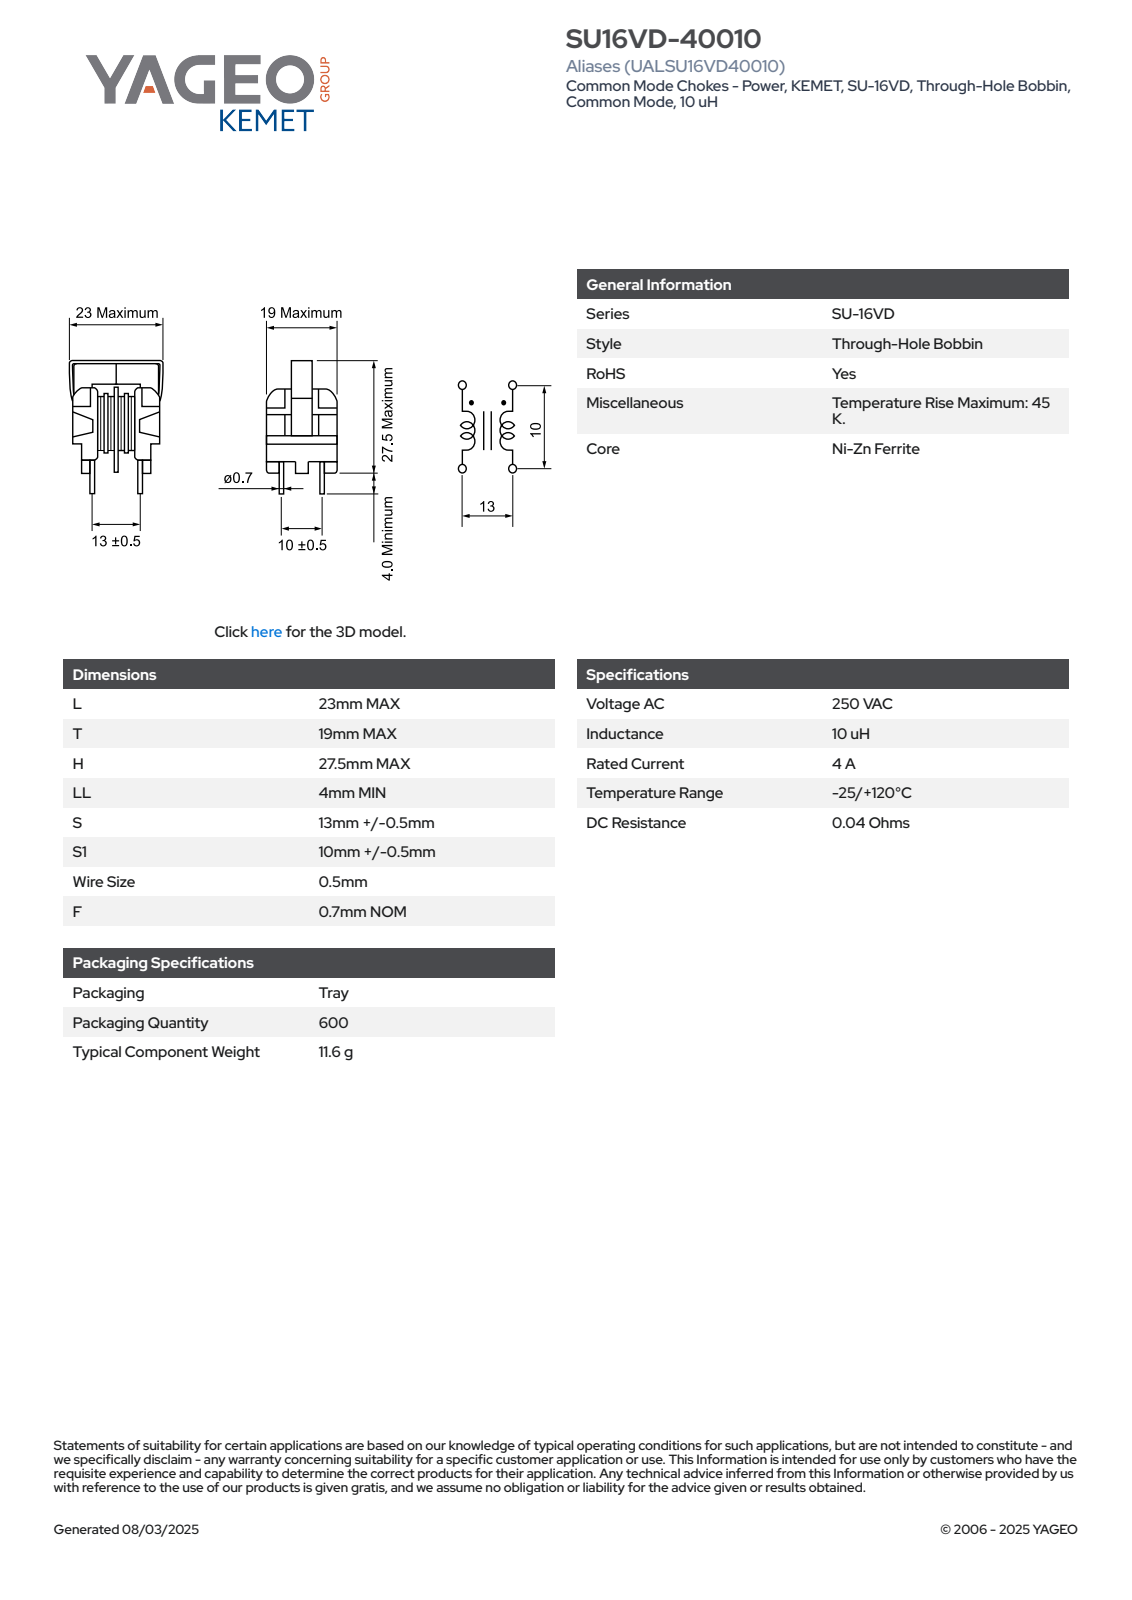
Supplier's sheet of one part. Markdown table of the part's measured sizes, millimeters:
| quantity | value |
| --- | --- |
| part name | SU16VD(MAX-LOGO) |
| STEP written by | SolidWorks 2018 (AUTOMOTIVE_DESIGN) |
| units | millimeters |
| bodies | 4 solids, 521 faces (232 planar, 211 cylindrical, 78 other) |
| overall size | 32 × 23 × 19 |
| volume | 4 325 mm³ |
| surface area | 5 415 mm² |
| round bosses / shafts (diameter × count) | 0.7 × 4 |
| partial cylindrical surfaces (radius × count) | 0.36 × 48, 0.5 × 32, 0.8 × 12, 0.4 × 8, 0.2 × 4, 0.3 × 2, 2.5 × 2, 3.5 × 2 |
| main face-to-face distances | 5, 4.4, 5.4, 1, 5.2, 7, 0.5, 0.4, 10.6, 11 |
